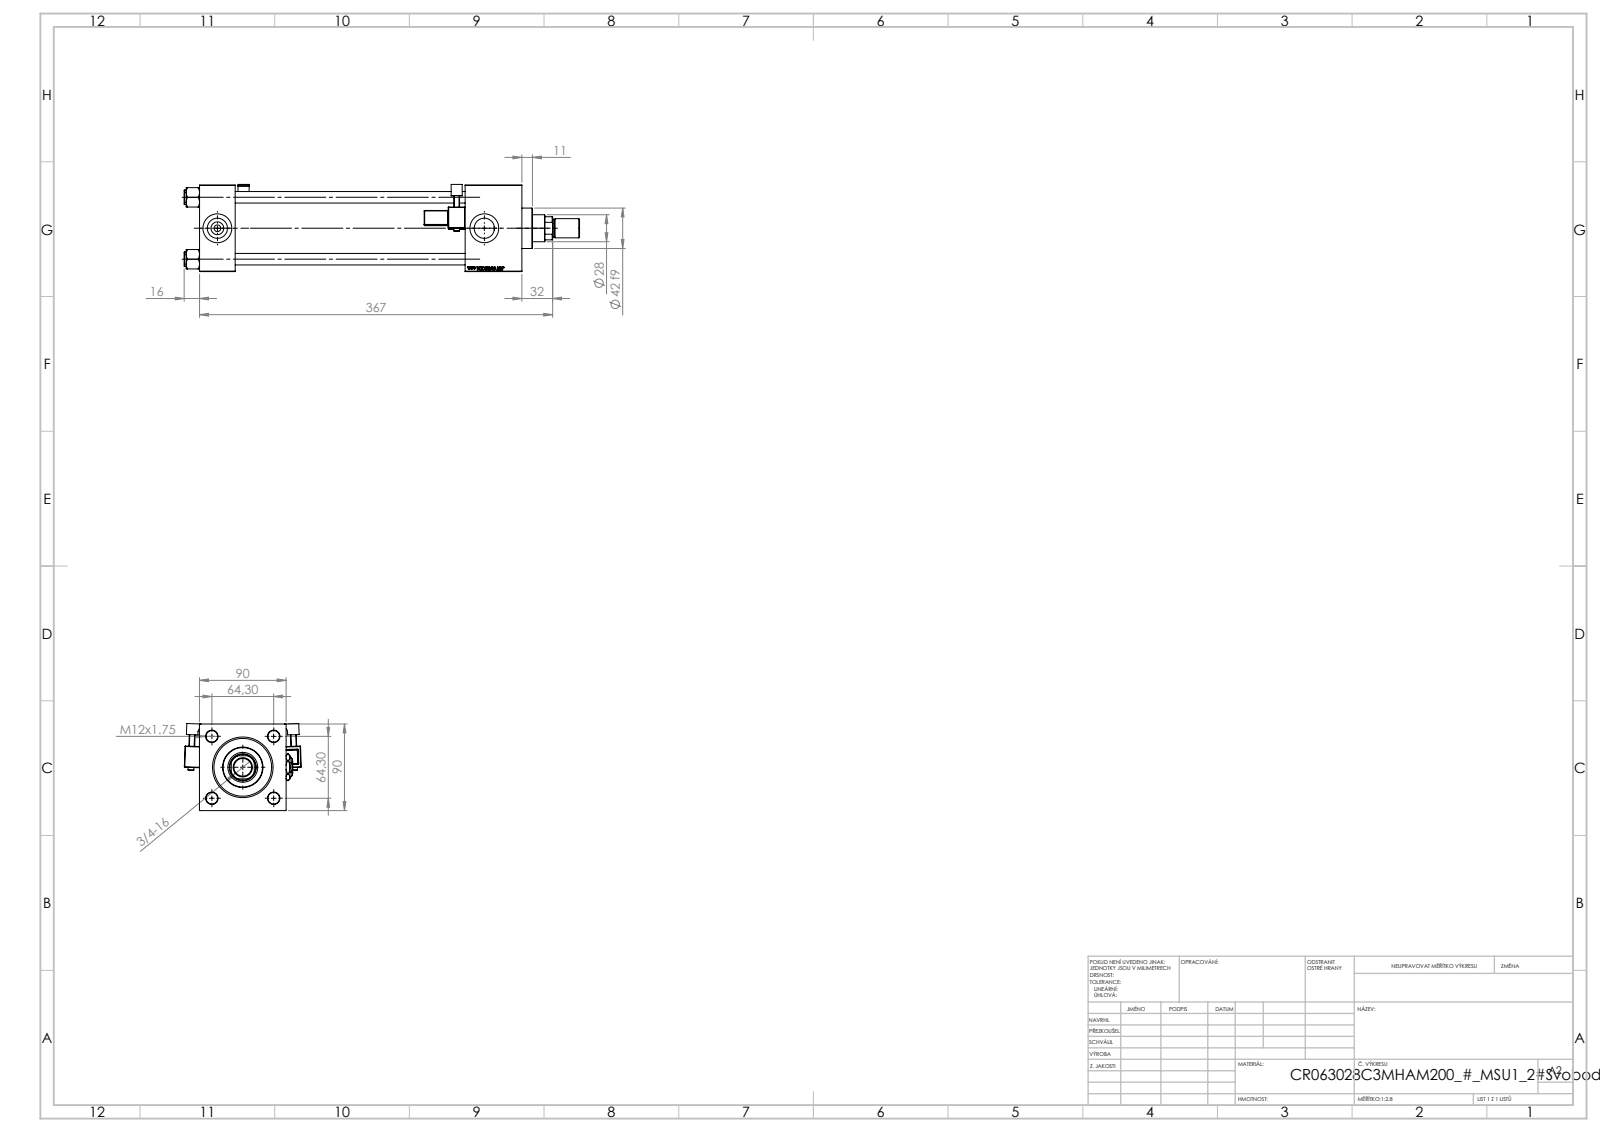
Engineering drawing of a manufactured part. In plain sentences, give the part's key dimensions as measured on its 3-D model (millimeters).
The part is named "V215CR_C_Body; Zatka_pro_OIL_PORT; ROD_END_AH; V215CR_MSU (+4 more)". Its 3-D file was written by "SolidWorks 2019 (CONFIG_CONTROL_DESIGN)". It is 16 solids with 1418 faces: 636 planar, 162 cylindrical and 620 other. Overall it measures 411 by 121.57 by 90.53 millimeters. Its volume is 1 295 000 cubic millimeters and its surface area 316 239 square millimeters. Round holes: 4 of diameter 12, 2 of diameter 7, 2 of diameter 20.96, 2 of diameter 30, 1 of diameter 18.5, 1 of diameter 28, 1 of diameter 31, 1 of diameter 50, 1 of diameter 60, 1 of diameter 63. Round bosses or shafts: 4 of diameter 15, 2 of diameter 6, 1 of diameter 69, 1 of diameter 42, 1 of diameter 20, 1 of diameter 18. Partial cylindrical surfaces (rounded edges, fillets, slot ends): 48 of radius 0.5, 2 of radius 1, 2 of radius 2.5, 2 of radius 4, 1 of radius 13.5. The main face-to-face distances are 90, 37, 335, 298, 276, 239, 59, 306.3, 269.3, 30.3. The hole center spacings are 45.47, 64.3, 90.93, 277.5.
